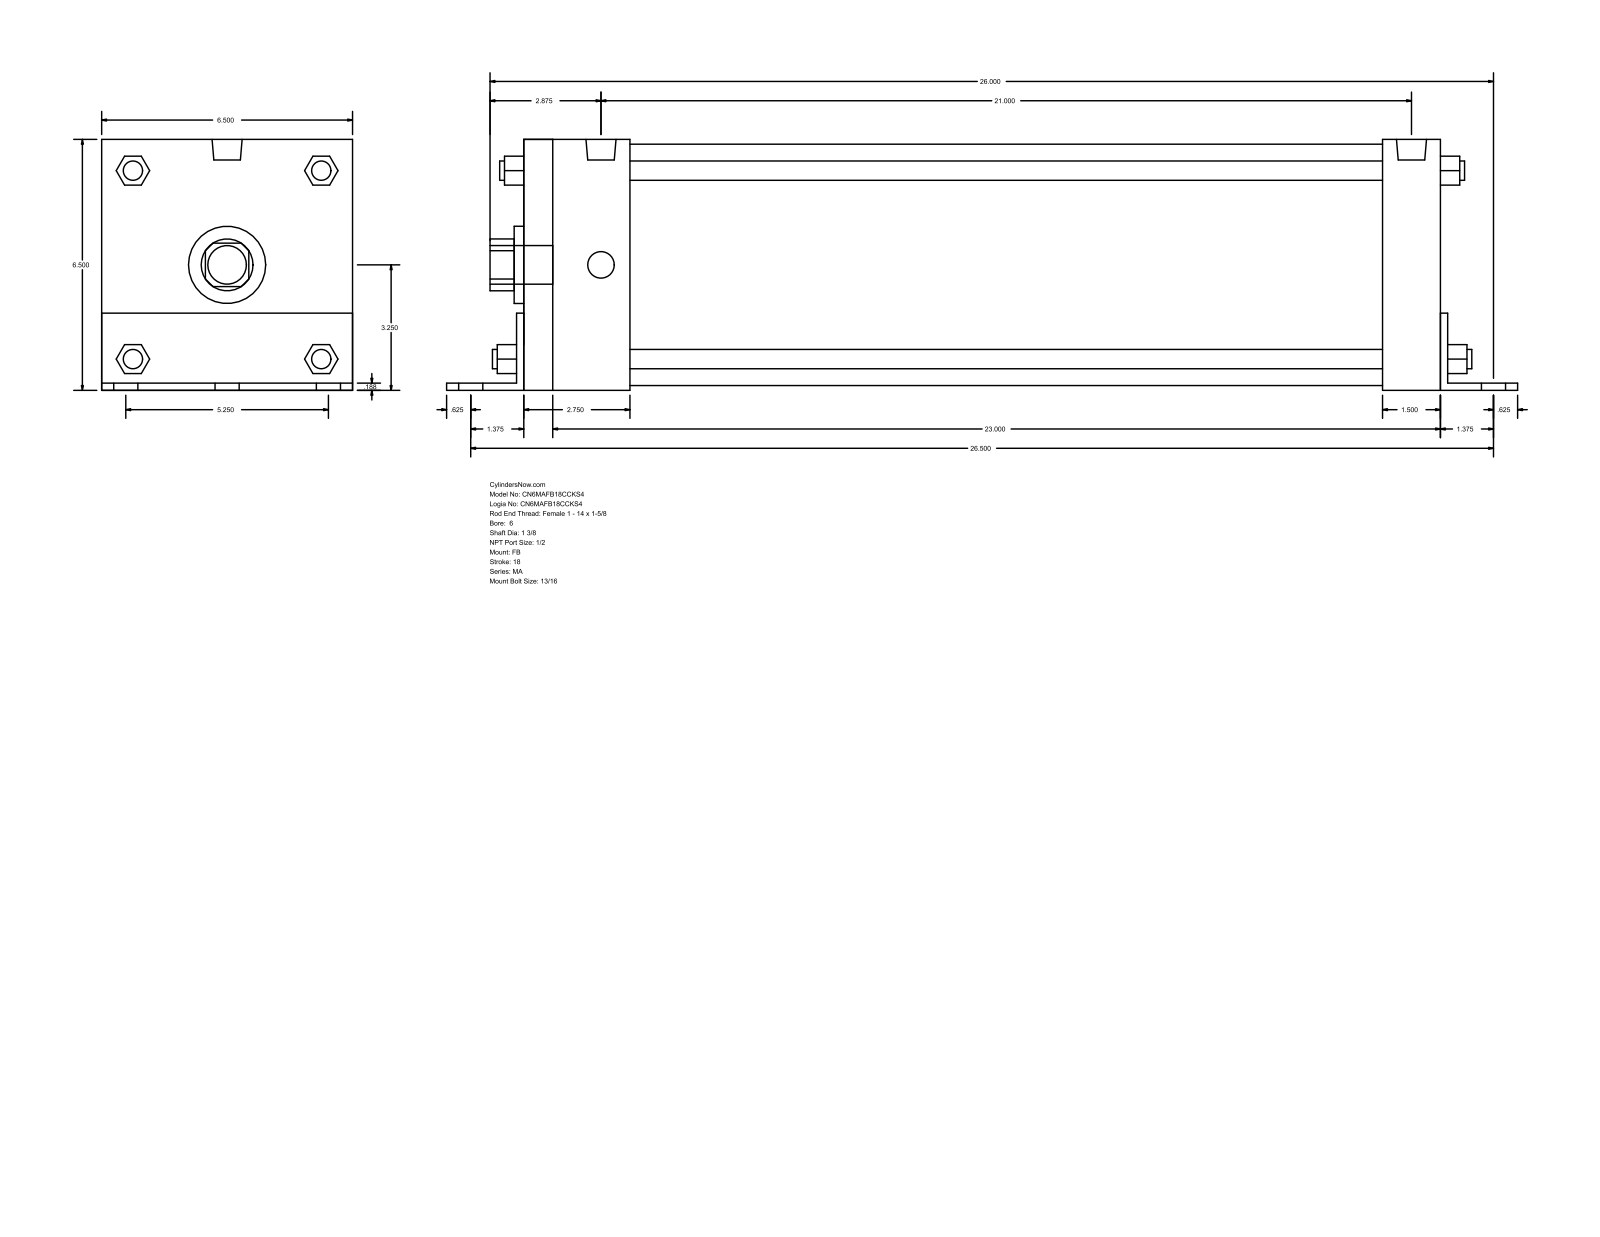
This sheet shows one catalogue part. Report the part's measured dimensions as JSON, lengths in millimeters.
{"part_name": "MA_FB__0600_1.375", "step_written_by": "GSSL Pune (CONFIG_CONTROL_DESIGN)", "units": "millimeters", "bodies": {"solids": 0, "faces": 140, "planar": 105, "cylindrical": 35, "other": 0}, "overall_size": [701.67, 165.15, 165.1], "round_holes": [[34.92, 1], [50.8, 1], [158.75, 1]], "round_bosses_or_shafts": [[20.64, 6], [17.46, 4], [12.7, 4], [19.77, 2], [25.4, 1]], "partial_cylinders_radius": [[17.06, 1], [32.05, 1]], "face_to_face_distances": [165.1, 4.76, 600.07, 165.15, 4.71, 160.39, 4.77, 38.1, 604.84, 609.6]}
